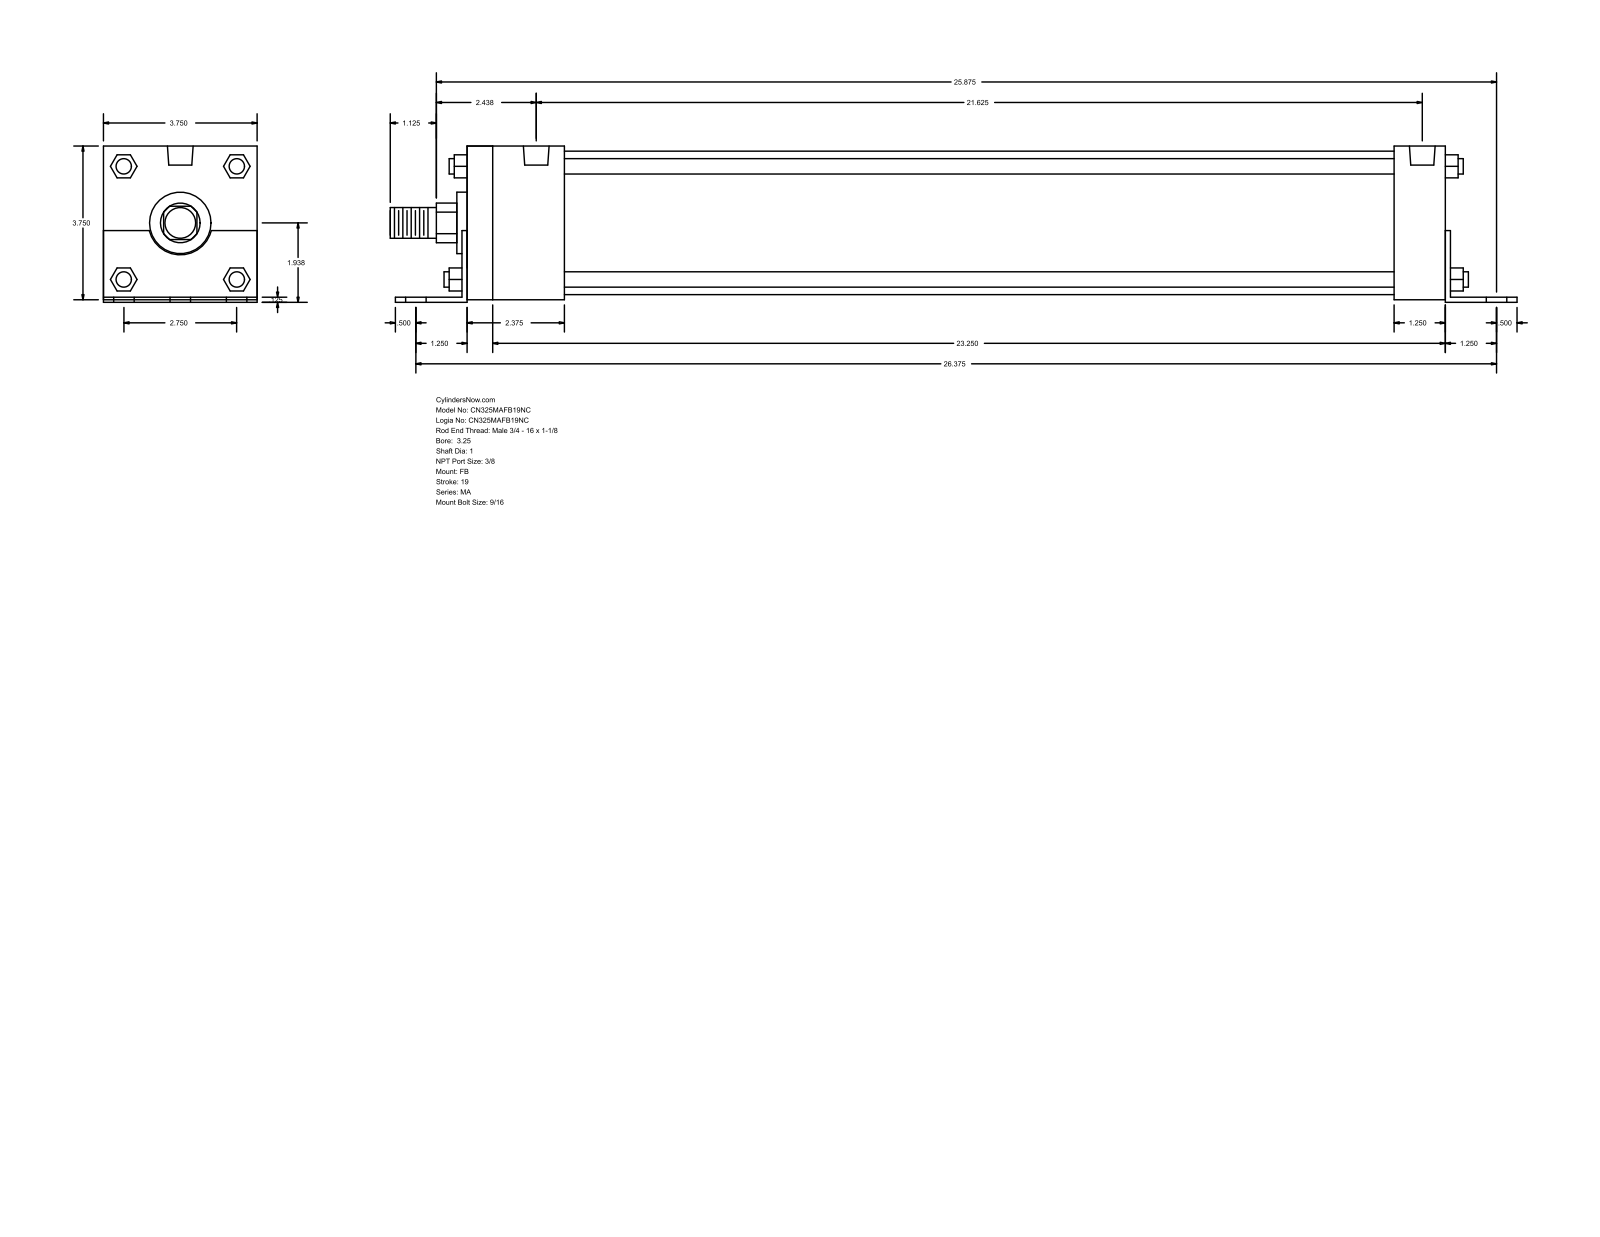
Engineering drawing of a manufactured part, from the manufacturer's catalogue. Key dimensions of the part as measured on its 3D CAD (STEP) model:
Part name (STEP PRODUCT): MA_FB__0325_1
STEP written by: GSSL Pune (CONFIG_CONTROL_DESIGN)
Units: millimetres
Bodies: 0 solids, 140 faces (105 planar, 35 cylindrical, 0 other)
Overall size (bounding box): 698.5 × 96.84 × 95.25
Round holes (diameter × count): ⌀14.29 ×6, ⌀11.11 ×4, ⌀15.93 ×2
Round bosses / shafts (diameter × count): ⌀9.53 ×4, ⌀88.9 ×1, ⌀38.1 ×1, ⌀25.4 ×1, ⌀19.05 ×1
Partial cylindrical surfaces — rounded edges, fillets, slot ends (radius × count): R12.29 ×1, R19.81 ×1
Main face-to-face distances: 95.24, 3.17, 1.59, 96.83, 1.58, 93.66, 609.6, 606.43, 612.77, 577.85
Hole centre spacings: 34.92, 670.84, 669.93, 57.78, 61.65, 69.84, 82.38, 86.71
